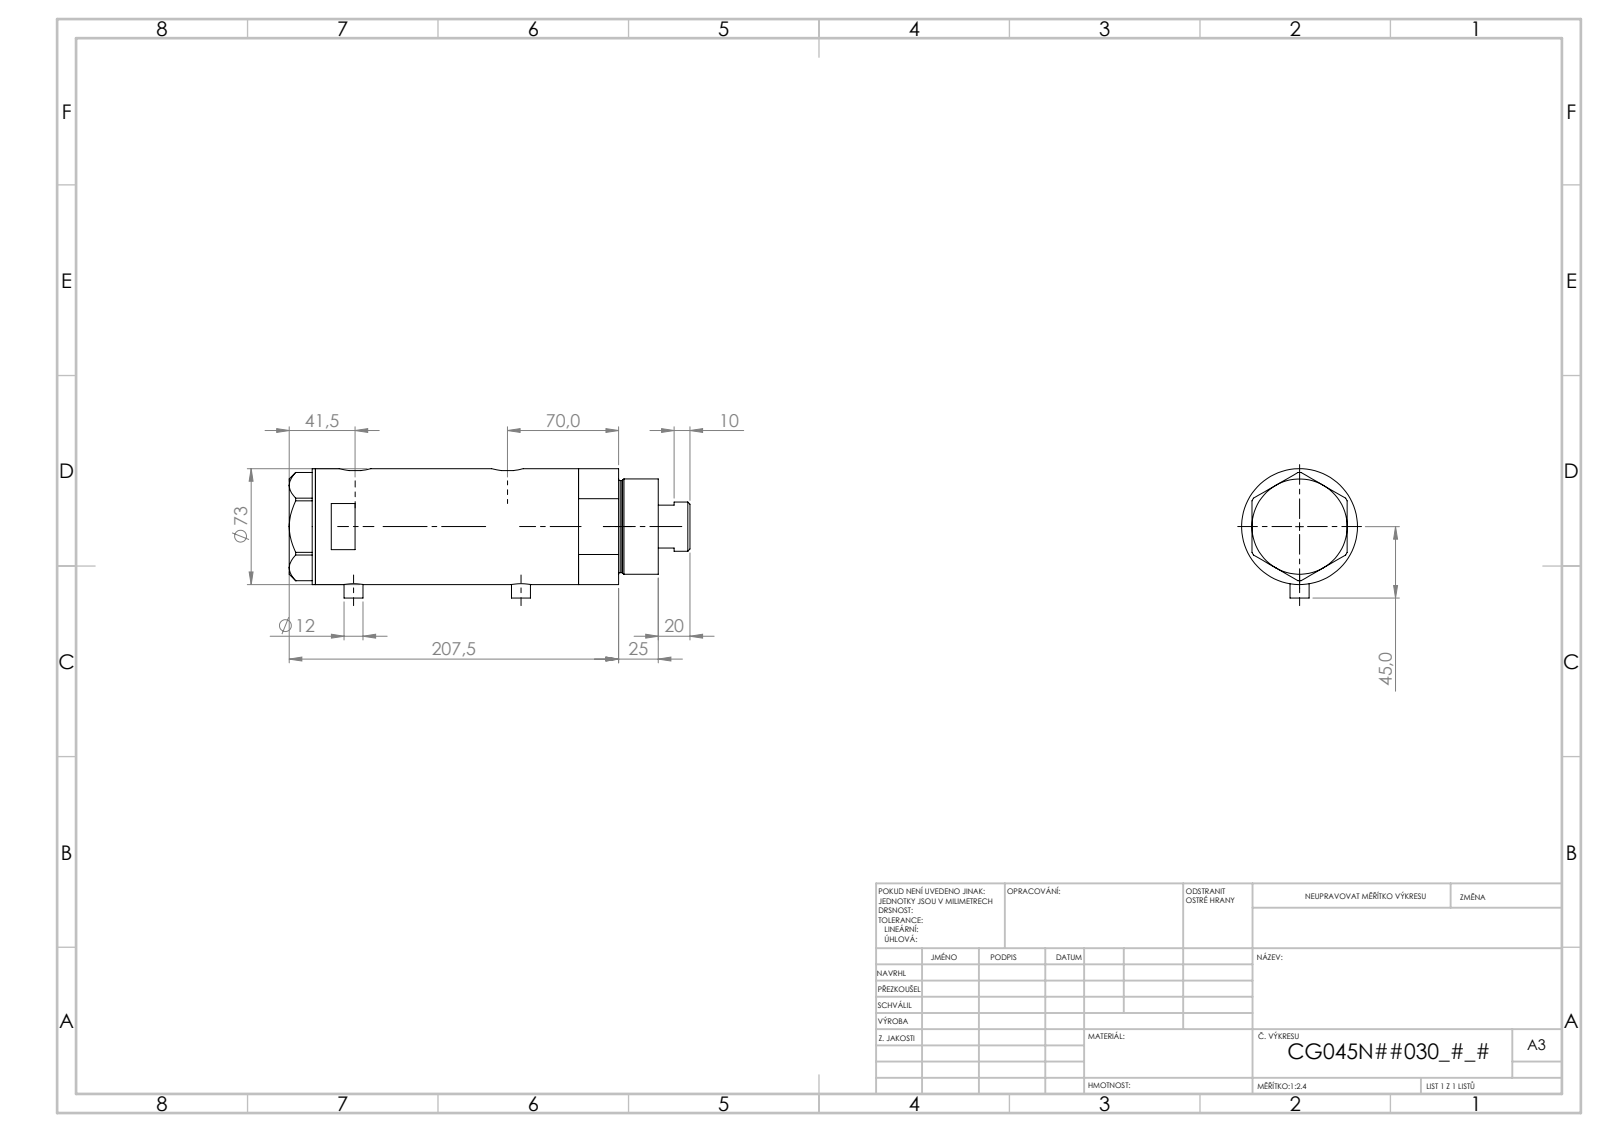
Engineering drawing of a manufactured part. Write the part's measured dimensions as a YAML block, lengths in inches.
part_name: "V270CG_VC; V270CG_FRONT; V270CG_MIDDLE; V270CG_BACK"
step_written_by: "SolidWorks 2019 (CONFIG_CONTROL_DESIGN)"
units: inches
bodies: {solids: 4, faces: 125, planar: 50, cylindrical: 55, other: 20}
overall_size: [8.721, 2.917, 2.874]
volume: 46.91
surface_area: 207.8
round_holes:
  - {diameter: 0.197, count: 2}
  - {diameter: 0.492, count: 2}
  - {diameter: 0.518, count: 2}
  - {diameter: 0.413, count: 1}
  - {diameter: 1.26, count: 1}
  - {diameter: 1.319, count: 1}
  - {diameter: 1.772, count: 1}
  - {diameter: 1.89, count: 1}
  - {diameter: 2.52, count: 1}
round_bosses_or_shafts:
  - {diameter: 0.472, count: 2}
  - {diameter: 2.874, count: 1}
  - {diameter: 2.362, count: 1}
  - {diameter: 2.283, count: 1}
  - {diameter: 1.22, count: 1}
partial_cylinders:
  - {radius: 0.394, count: 2}
face_to_face_distances: [3.824, 0.65, 4.474, 7.284, 7.933, 3.459, 1.673, 1.024, 2.801, 6.26]
hole_center_spacings: [3.215, 0.039, 0.039, 0.335, 0.335, 2.841, 2.88, 2.88]
